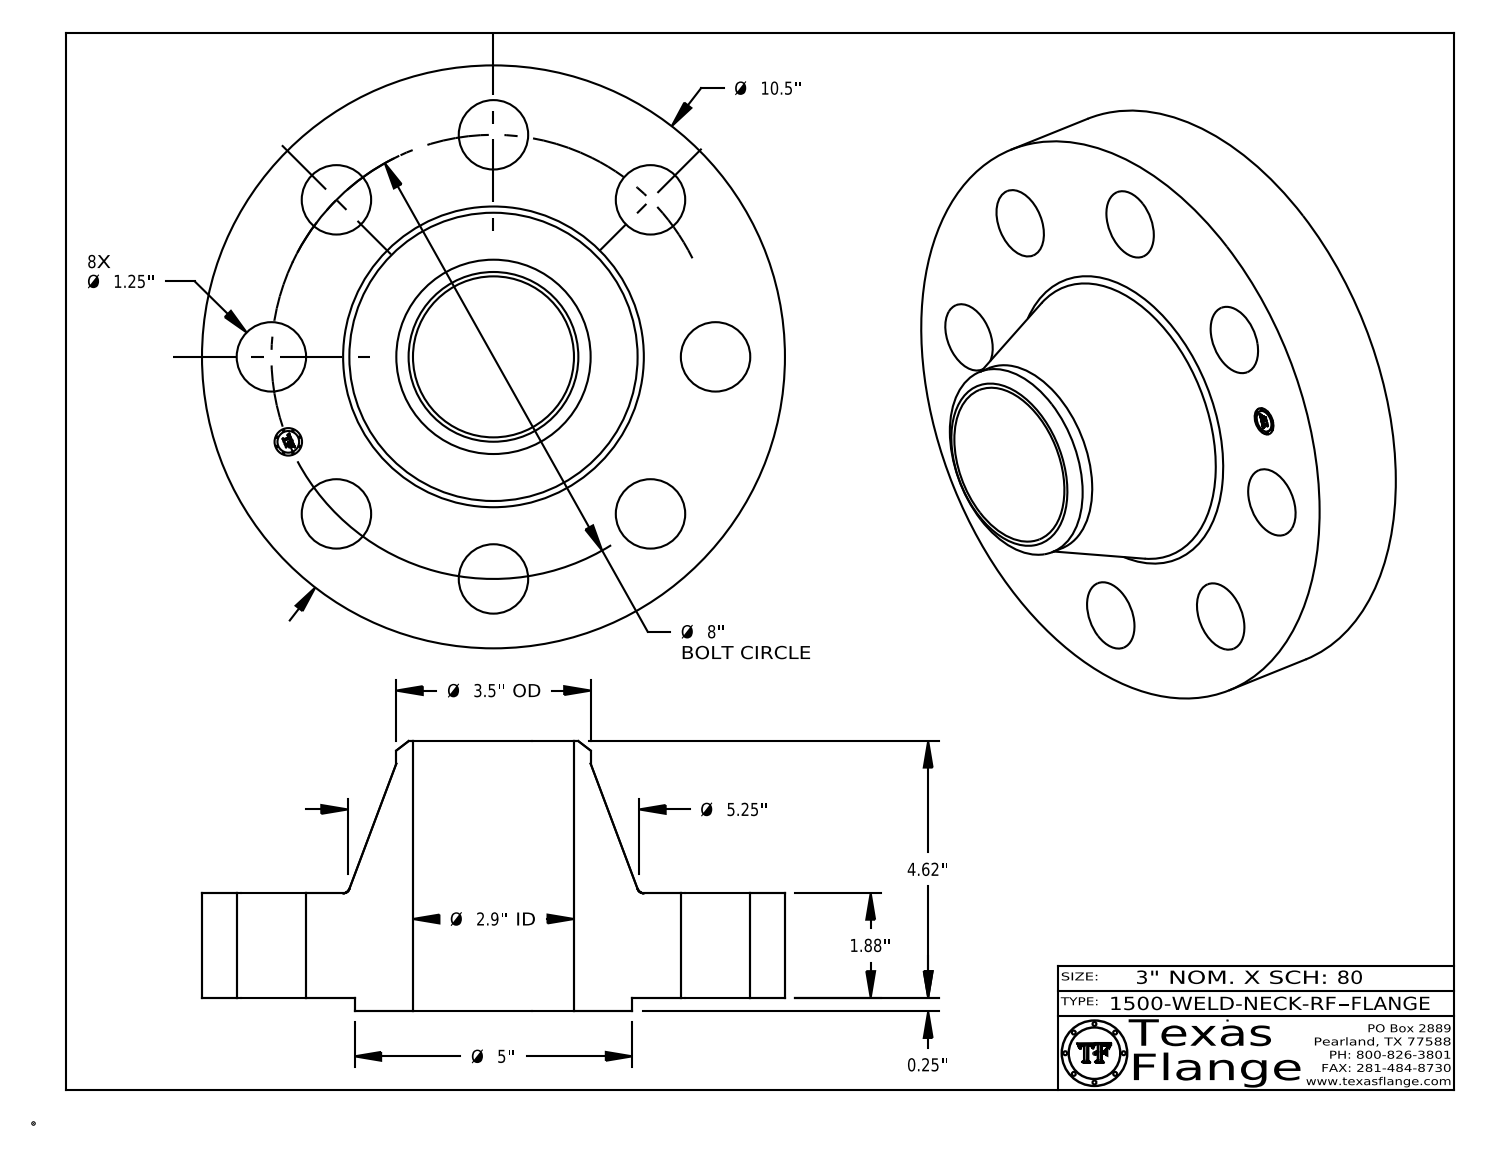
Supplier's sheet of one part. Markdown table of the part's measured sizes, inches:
| quantity | value |
| --- | --- |
| part name | 1500-WELD-NECK-RF |
| STEP written by | CATIA V5 STEP AP214 (AUTOMOTIVE_DESIGN) |
| units | inches |
| bodies | 1 solid, 419 faces (369 planar, 44 cylindrical, 6 other) |
| overall size | 10.5 × 10.5 × 4.87 |
| volume | 156.4 in³ |
| surface area | 334.9 in² |
| round holes (diameter × count) | 1.25 × 8, 0.495 × 1, 2.9 × 1 |
| round bosses / shafts (diameter × count) | 0.03 × 8, 10.5 × 1, 5 × 1, 3.5 × 1, 0.39 × 1 |
| main face-to-face distances | 1.88, 0.25, 2.13, 4.87, 4.62, 2.74, 0.015, 2.115, 1.865, 2.755 |
| hole center spacings | 4, 3.061, 5.657, 7.391, 1.561, 6.652, 7.846, 8 |
